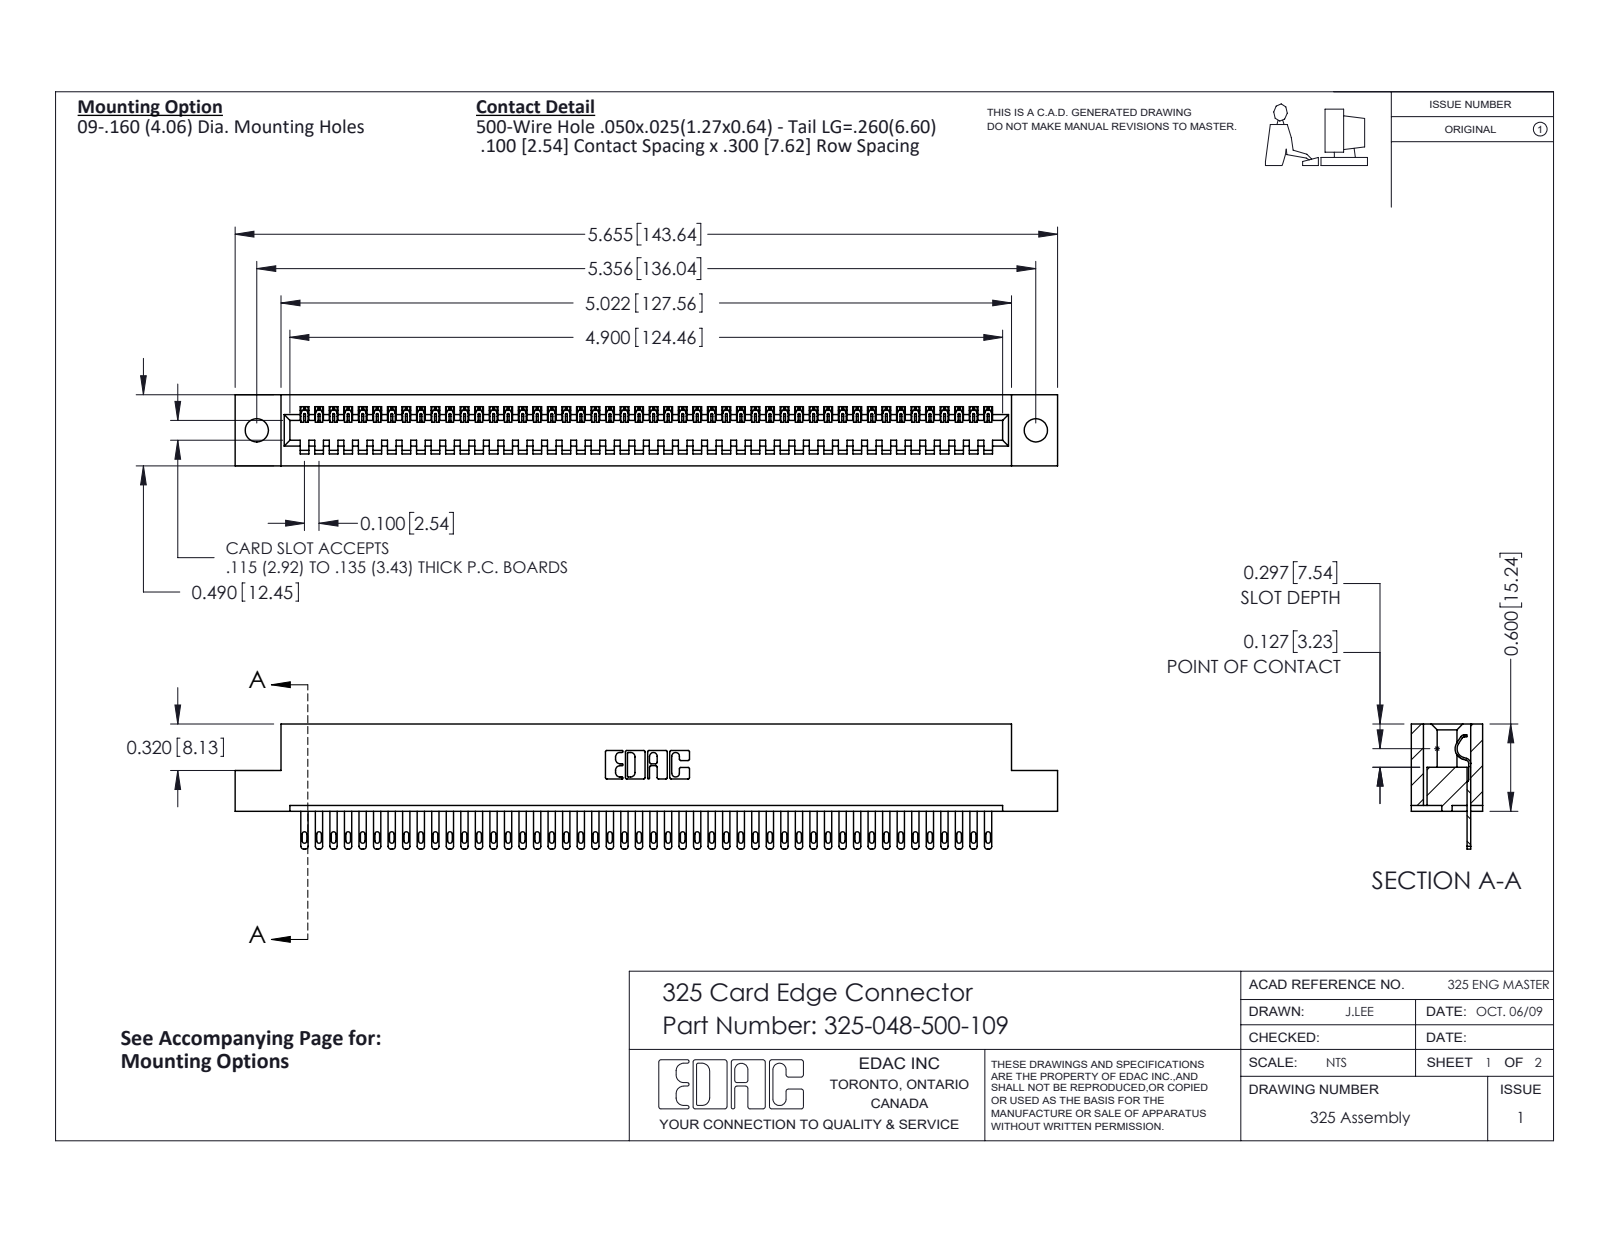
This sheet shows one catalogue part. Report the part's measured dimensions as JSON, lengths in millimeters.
{"part_name": "325-048-500-109; 325-292-001_325-293-100; 325 Part_.160 TH", "step_written_by": "SolidWorks 2016 (CONFIG_CONTROL_DESIGN)", "units": "millimeters", "bodies": {"solids": 49, "faces": 2706, "planar": 1798, "cylindrical": 908, "other": 0}, "overall_size": [143.6, 21.8, 12.4], "volume_mm3": 18070, "surface_area_mm2": 19860, "round_holes": [[4.1, 2]], "partial_cylinders_radius": [[0.2, 96], [0.4, 96], [0.5, 96], [0.3, 22], [0.2, 6], [0.8, 6], [0.7, 3], [0.4, 1]], "face_to_face_distances": [2.1, 10.3, 12.4, 7.6, 2.7, 9.7, 0.6, 8.3, 14.2, 6.7], "hole_center_spacings": [136]}
